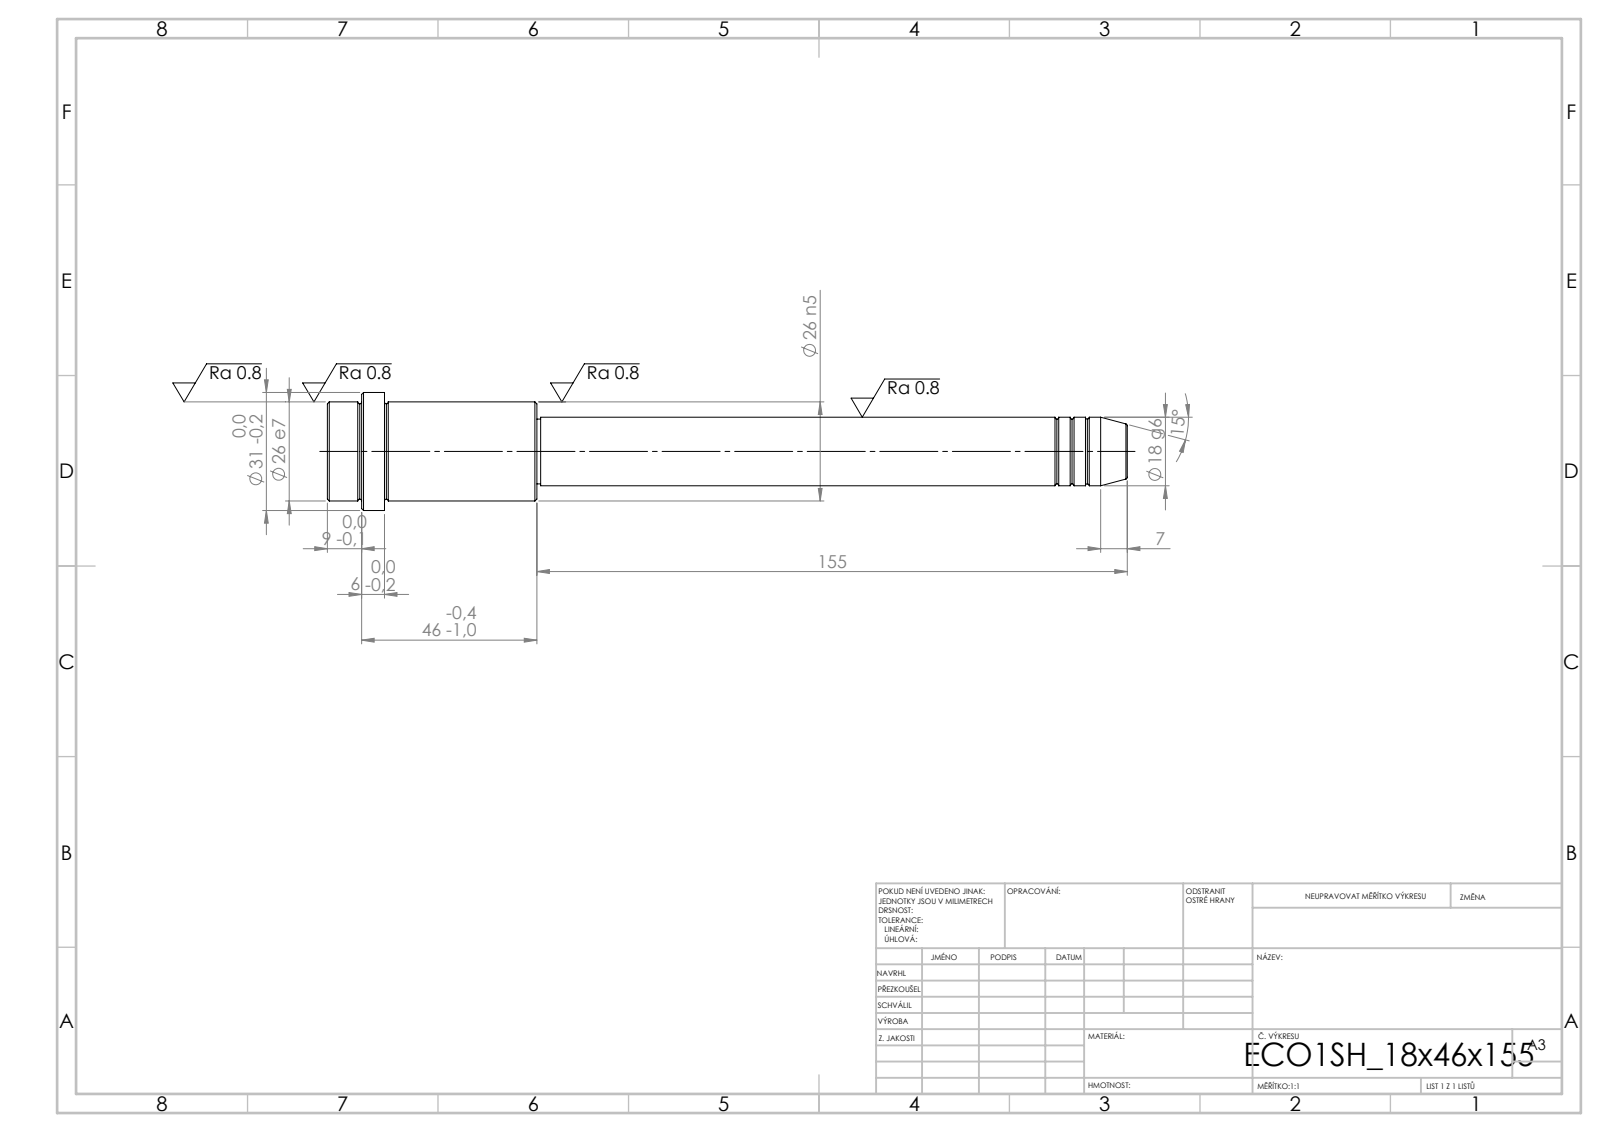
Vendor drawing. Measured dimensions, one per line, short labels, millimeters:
written by: SolidWorks 2019 (CONFIG_CONTROL_DESIGN)
unit: mm
bodies: 1 solid, 52 faces (6 planar, 16 cylindrical, 30 other)
size: 210 × 31 × 31
volume: 69 452 mm³; area: 14 881 mm²
bosses: 1× ⌀31, 1× ⌀26, 1× ⌀18, 1× ⌀17
face distances: 55, 40, 15, 46, 6, 9, 155, 195, 201, 210
